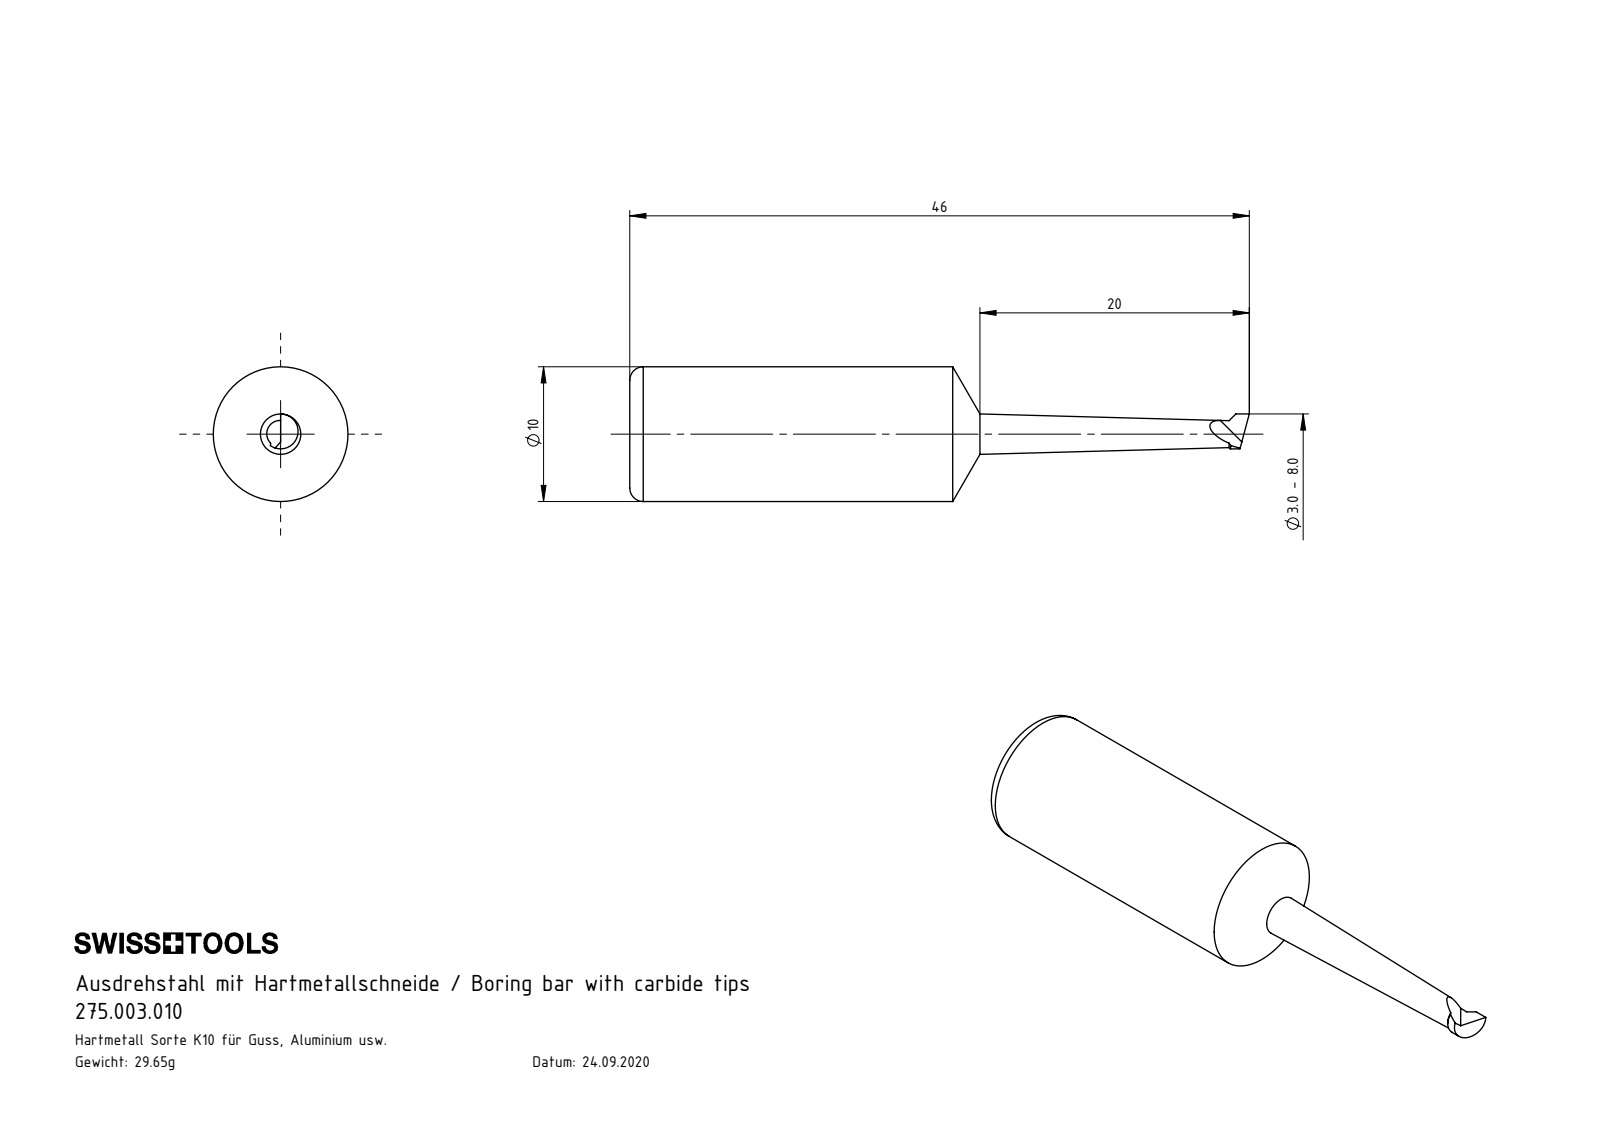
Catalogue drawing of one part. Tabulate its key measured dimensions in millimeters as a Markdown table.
| quantity | value |
| --- | --- |
| part name | U10.B03.001.020 |
| STEP written by | SolidWorks 2012 (CONFIG_CONTROL_DESIGN) |
| units | millimeters |
| bodies | 1 solid, 28 faces (3 planar, 3 cylindrical, 22 other) |
| overall size | 46.3 × 10 × 10 |
| volume | 2 076 mm³ |
| surface area | 1 079 mm² |
| round bosses / shafts (diameter × count) | 10 × 1 |
| partial cylindrical surfaces (radius × count) | 0.8 × 1 |
